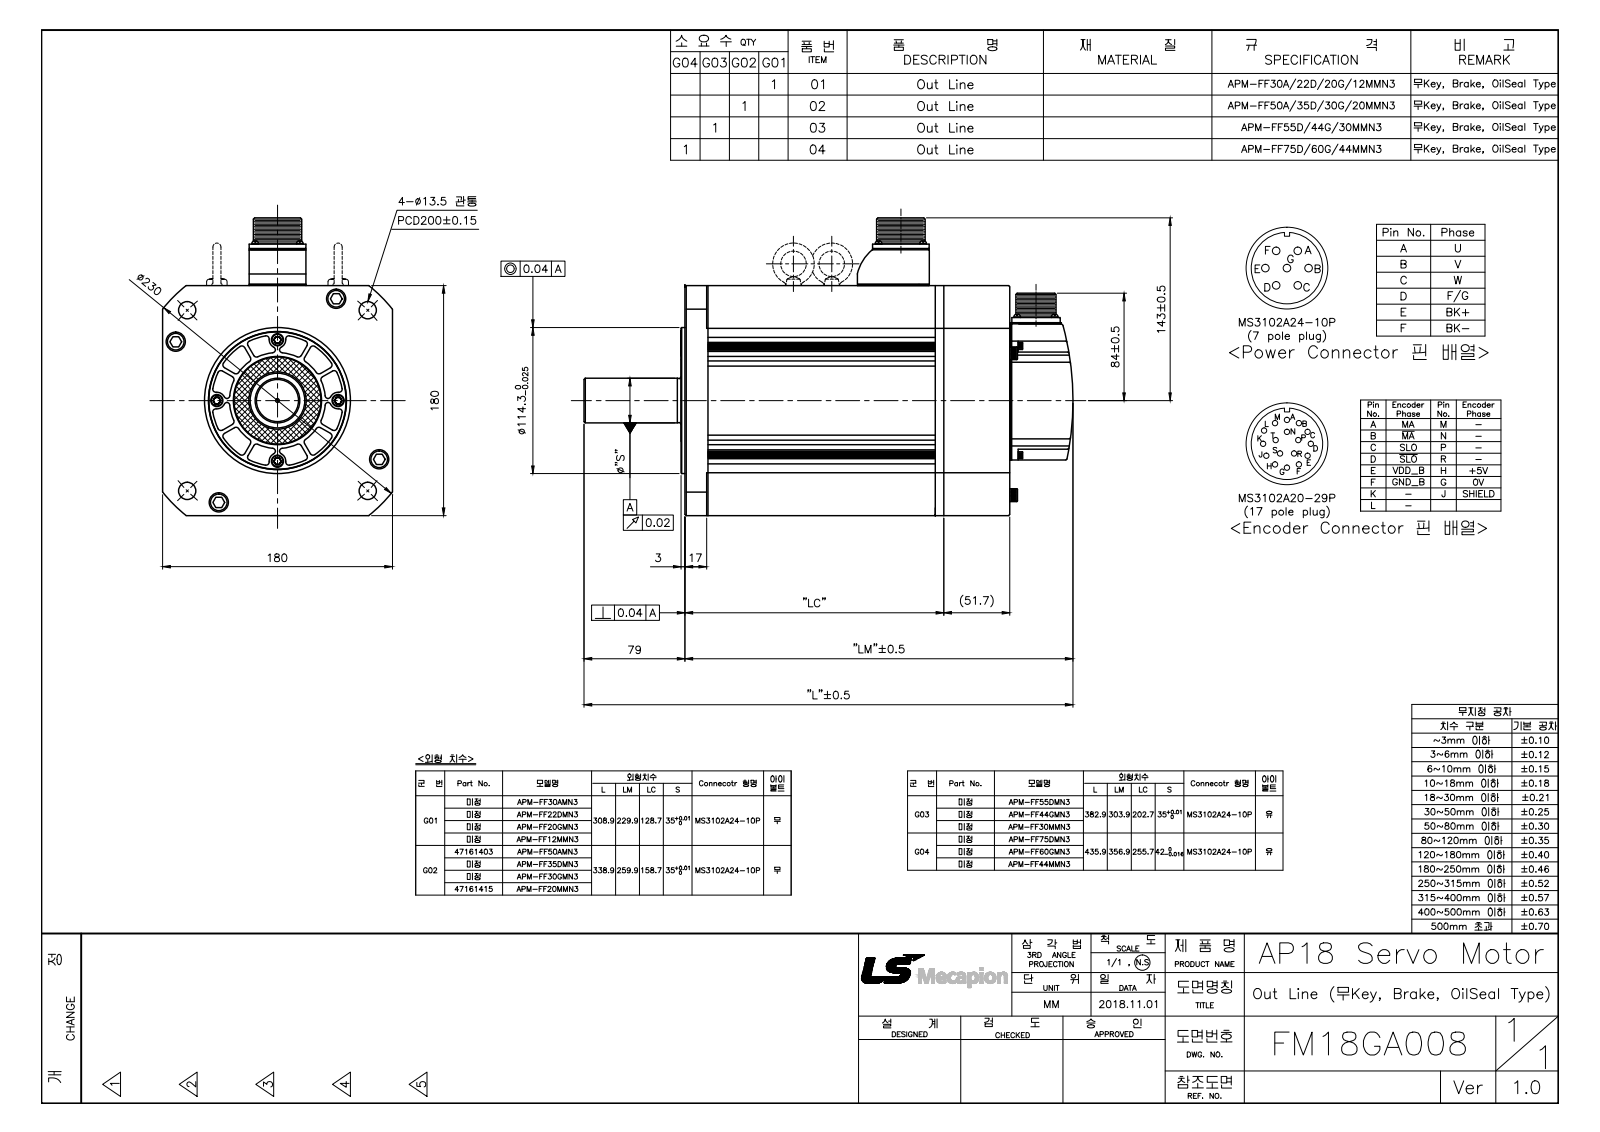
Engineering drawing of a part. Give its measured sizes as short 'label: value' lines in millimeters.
name: FM18GA002G04_Out Line(APM-FF75D_N,FF60G_N,FF44M_N)
written by: SolidWorks 2011 (AUTOMOTIVE_DESIGN)
unit: mm
bodies: 56 solids, 2344 faces (787 planar, 872 cylindrical, 685 other)
size: 384.5 × 232.5 × 180
volume: 7 737 000 mm³; area: 560 851 mm²
holes: 12× ⌀3, 8× ⌀2.5, 8× ⌀3.05, 8× ⌀6, 8× ⌀9.5, 6× ⌀6.8, 4× ⌀3.5, 4× ⌀3.6, 4× ⌀3.7, 4× ⌀5, 4× ⌀9, 4× ⌀9.2
bosses: 17× ⌀1.6, 8× ⌀5.4, 4× ⌀13.2, 4× ⌀13, 4× ⌀8.5, 4× ⌀8, 4× ⌀5.5, 4× ⌀3
rounds: 124× R0.5, 56× R2.5, 24× R4, 17× R2, 14× R1, 12× R4.5, 4× R6.5, 2× R0.3
face distances: 231, 180, 1, 18, 7.5, 33.5, 146.5, 8, 7, 10
hole spacings: 32.56, 74.42, 137.74, 1.06, 20.79, 22.49, 23.55, 26.28
